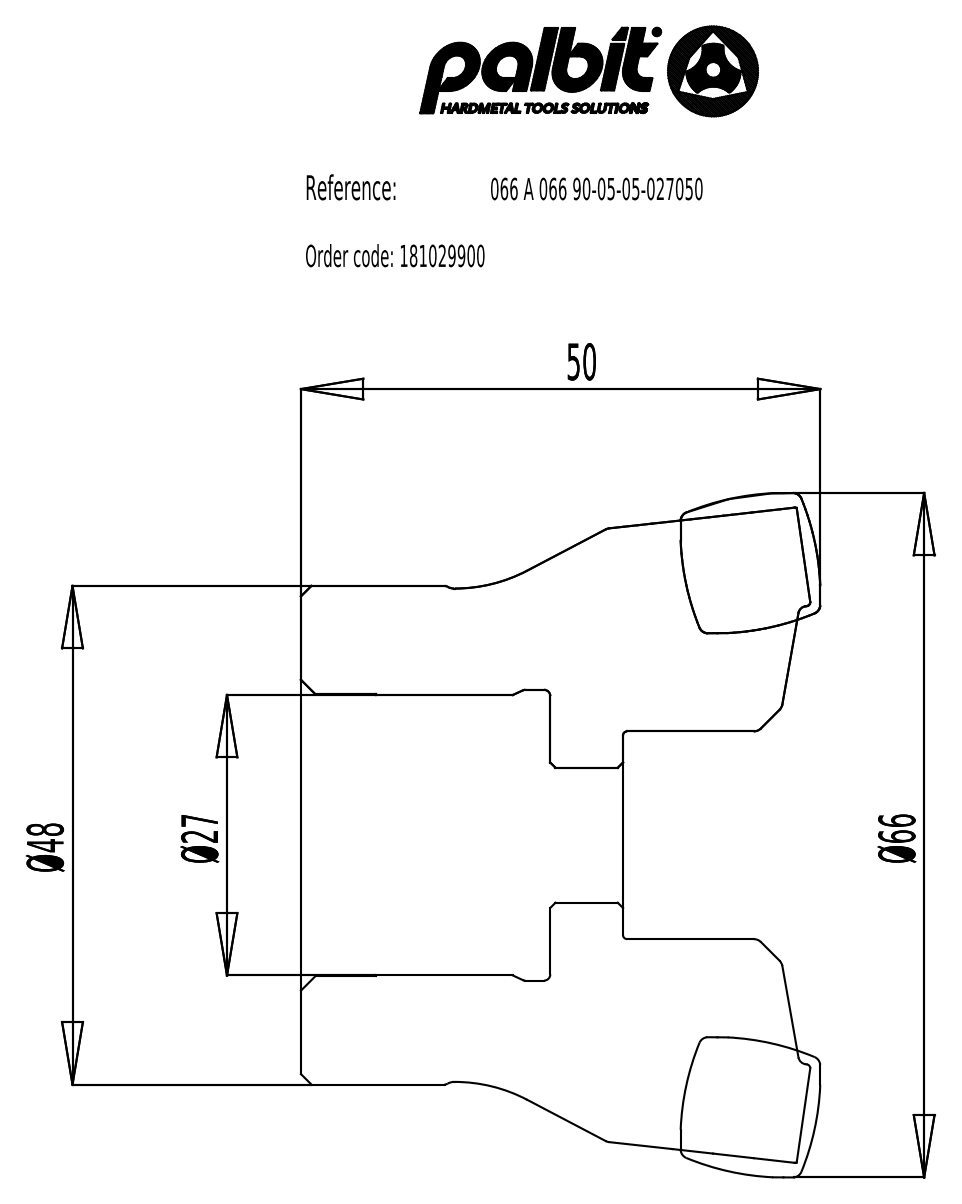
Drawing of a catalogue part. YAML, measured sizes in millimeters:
part_name: "CUT PROFILE - 181029900; CUT^CUT PROFILE - 181029900; NOCUT^CUT PROFILE - 181029900"
step_written_by: "SolidWorks 2015 (CONFIG_CONTROL_DESIGN)"
units: millimeters
bodies: {solids: 2, faces: 56, planar: 6, cylindrical: 7, other: 43}
overall_size: [65.9, 65.9, 49.99]
volume: 116765
surface_area: 23807
round_holes:
  - {diameter: 13, count: 1}
  - {diameter: 20, count: 1}
  - {diameter: 27, count: 1}
  - {diameter: 27.12, count: 1}
  - {diameter: 28, count: 1}
round_bosses_or_shafts:
  - {diameter: 48, count: 1}
  - {diameter: 47.5, count: 1}
face_to_face_distances: [24, 12.55, 36.55, 13.44, 25.99, 49.99, 18.99, 5.55, 7, 31]
